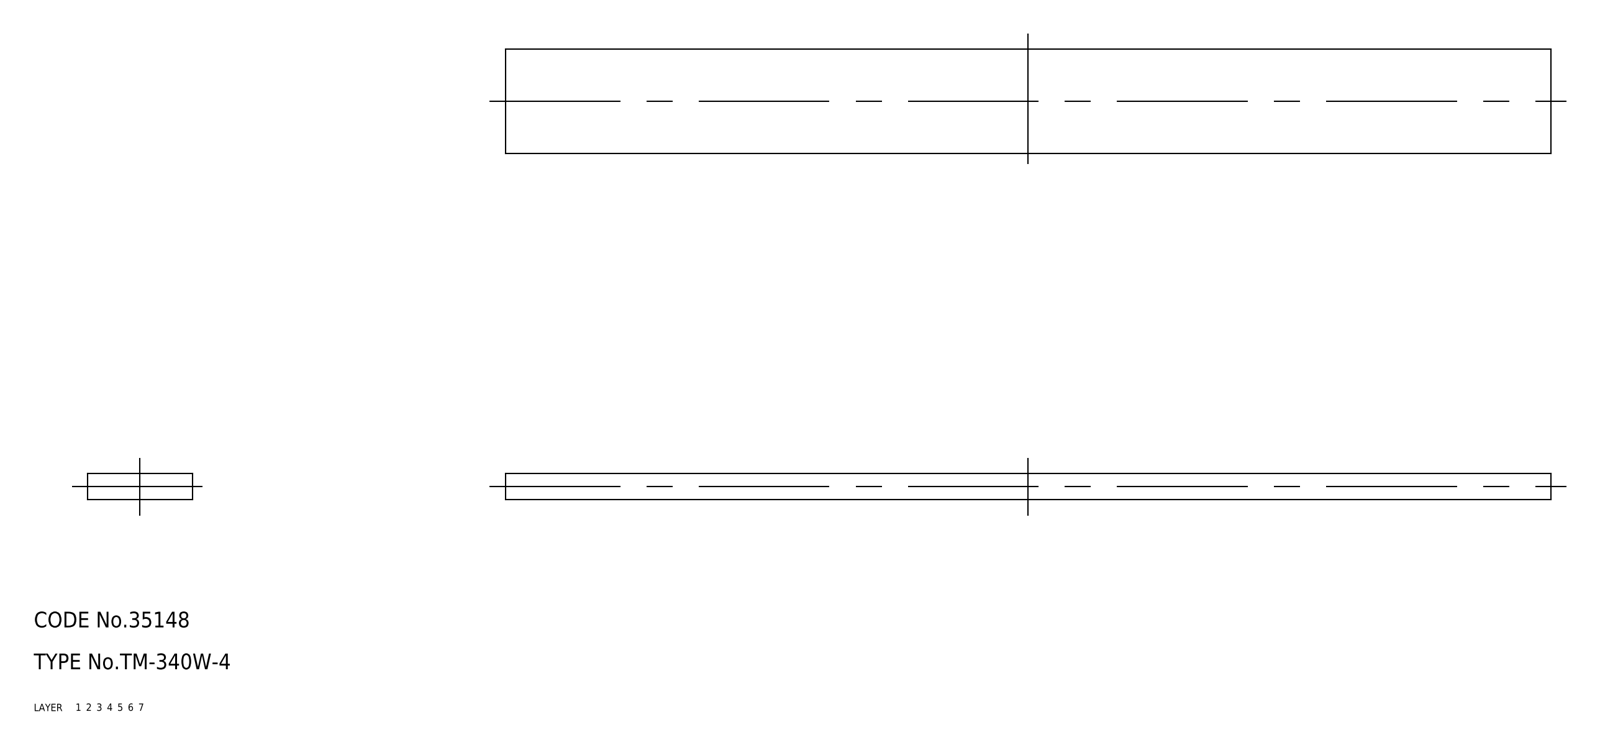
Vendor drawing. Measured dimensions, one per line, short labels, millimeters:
name: rubber foam; TM_340W_4
written by: SolidWorks 2015 (AUTOMOTIVE_DESIGN)
unit: mm
bodies: 1 solid, 6 faces (6 planar, 0 cylindrical, 0 other)
size: 200 × 20 × 5
volume: 20 000 mm³; area: 10 200 mm²
face distances: 5, 20, 200
